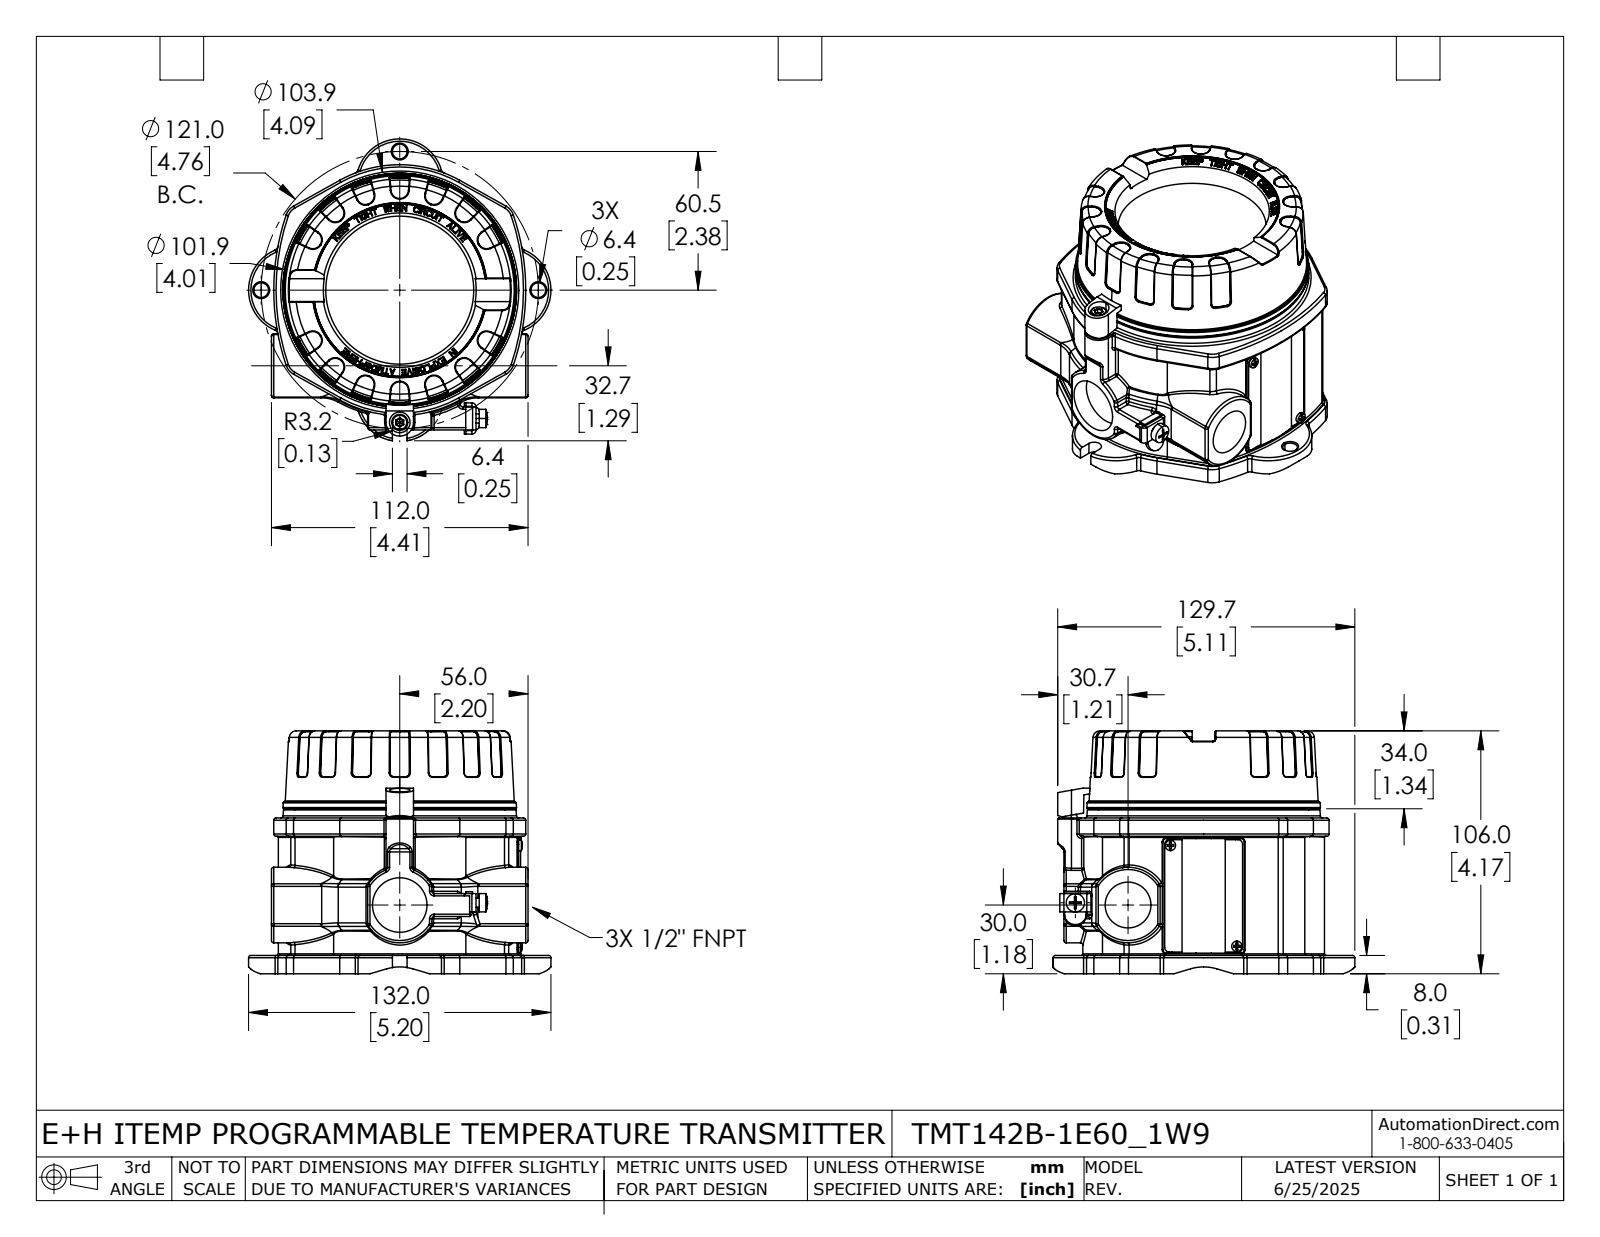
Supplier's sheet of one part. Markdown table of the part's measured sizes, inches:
| quantity | value |
| --- | --- |
| part name | TMT142B-1E60_1W9 |
| STEP written by | SolidWorks 2021 (AUTOMOTIVE_DESIGN) |
| units | inches |
| bodies | 1 solid, 2926 faces (1711 planar, 512 cylindrical, 703 other) |
| overall size | 5.197 × 5.186 × 4.173 |
| volume | 50.94 in³ |
| surface area | 171.5 in² |
| round holes (diameter × count) | 0.252 × 3, 0.165 × 2, 0.126 × 1, 0.169 × 1, 0.177 × 1, 0.228 × 1, 0.354 × 1, 0.787 × 1, 0.937 × 1, 3.161 × 1 |
| round bosses / shafts (diameter × count) | 0.177 × 2, 0.157 × 2, 0.315 × 1, 0.276 × 1 |
| partial cylindrical surfaces (radius × count) | 0.012 × 113, 0.039 × 67, 0.063 × 28, 0.15 × 28, 0.079 × 21, 0.02 × 10, 0.009 × 6, 0.028 × 6 |
| main face-to-face distances | 2.677, 2.402, 0.276, 1.358, 3.76, 1.083, 0.059, 1.146, 0.063, 2.614 |
| hole center spacings | 2.382, 2.604, 3.291, 3.369, 0.906, 1.051, 1.331, 2.272 |
